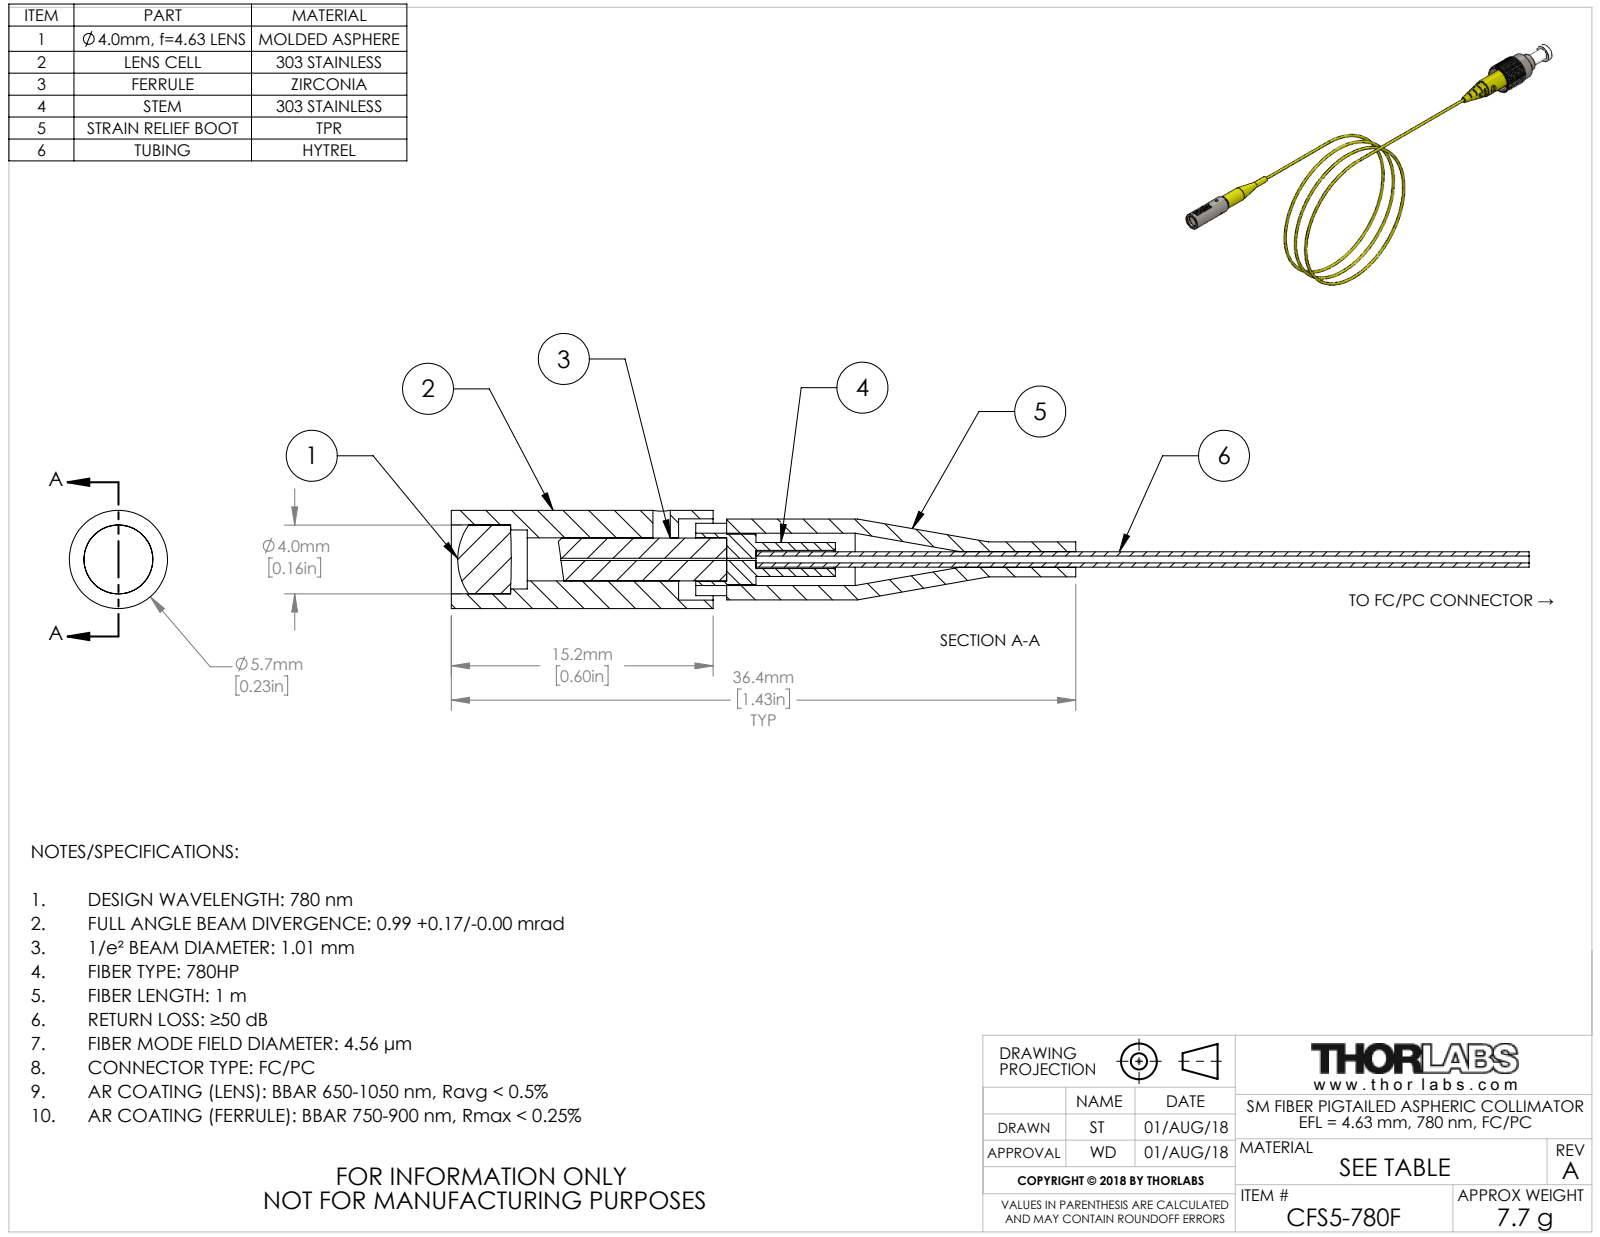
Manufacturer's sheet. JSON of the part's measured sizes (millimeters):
{"part_name": "TTN155843-E0W", "step_written_by": "SolidWorks 2018 (AUTOMOTIVE_DESIGN)", "units": "millimeters", "bodies": {"solids": 6, "faces": 117, "planar": 29, "cylindrical": 75, "other": 13}, "overall_size": [62.73, 5.71, 5.71], "volume_mm3": 534, "surface_area_mm2": 1309, "round_holes": [[1.02, 3], [0.4, 1], [0.91, 1], [1.06, 1], [2.5, 1], [2.54, 1], [3.05, 1], [3.43, 1], [4.01, 1], [4.72, 1]], "round_bosses_or_shafts": [[5.71, 1], [4.7, 1], [4, 1], [2.93, 1], [2.49, 1], [2.03, 1], [1.98, 1], [0.9, 1]], "partial_cylinders_radius": [[2.23, 1]], "face_to_face_distances": [16.03, 2.8, 13.23, 0.76, 2.28, 0.79, 2.01, 15.24, 1.8, 1.01]}
